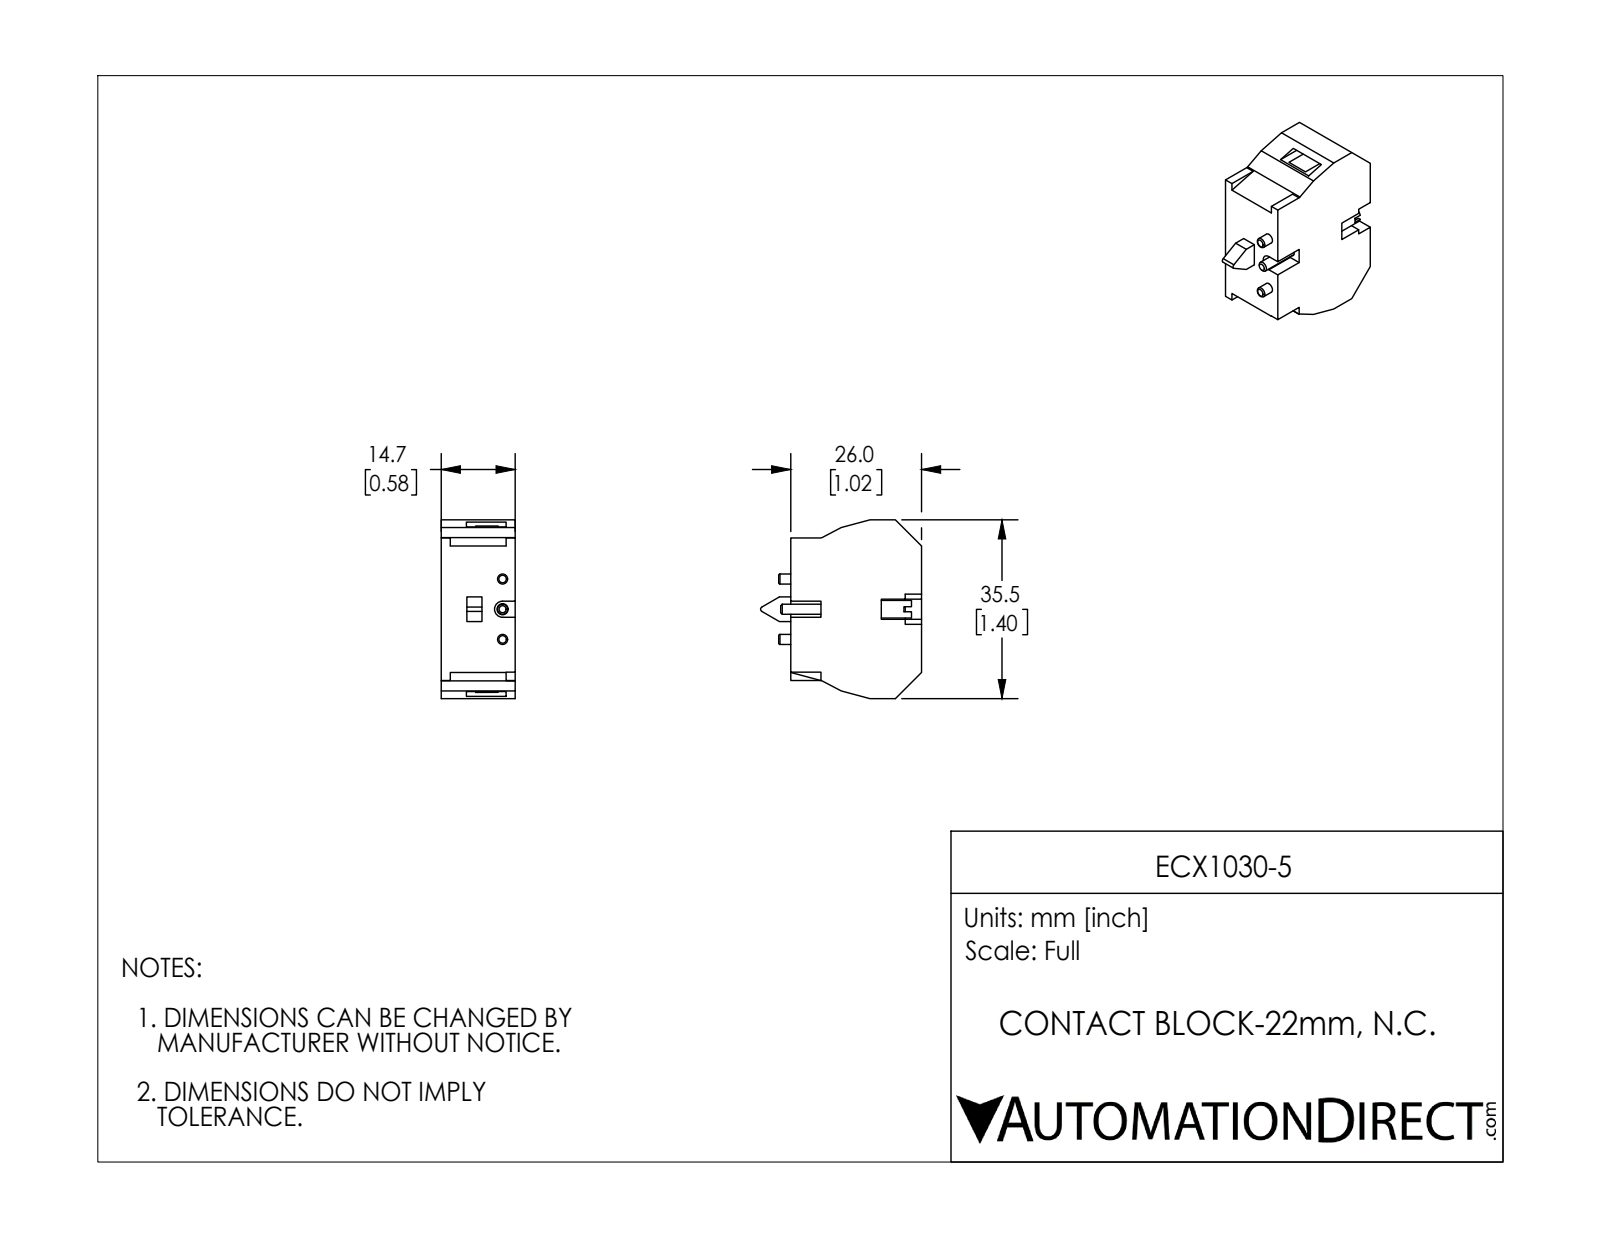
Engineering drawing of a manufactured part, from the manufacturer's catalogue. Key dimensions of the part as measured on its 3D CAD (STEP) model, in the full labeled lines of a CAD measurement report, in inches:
Part name (STEP PRODUCT): ECX1030-5
STEP written by: SolidWorks 2016 (AUTOMOTIVE_DESIGN)
Units: inches
Bodies: 1 solid, 93 faces (75 planar, 14 cylindrical, 4 other)
Overall size (bounding box): 1.399 × 1.26 × 0.579
Volume: 0.651 in³ · Surface area: 6.736 in²
Round holes (diameter × count): ⌀0.079 ×2, ⌀0.087 ×1
Partial cylindrical surfaces — rounded edges, fillets, slot ends (radius × count): R0.02 ×1, R0.063 ×1, R0.079 ×1
Main face-to-face distances: 0.579, 1.024, 0.269, 0.309, 0.018, 0.508, 0.27, 1.129, 0.037, 1.381
Hole centre spacings: 0.236, 0.472
